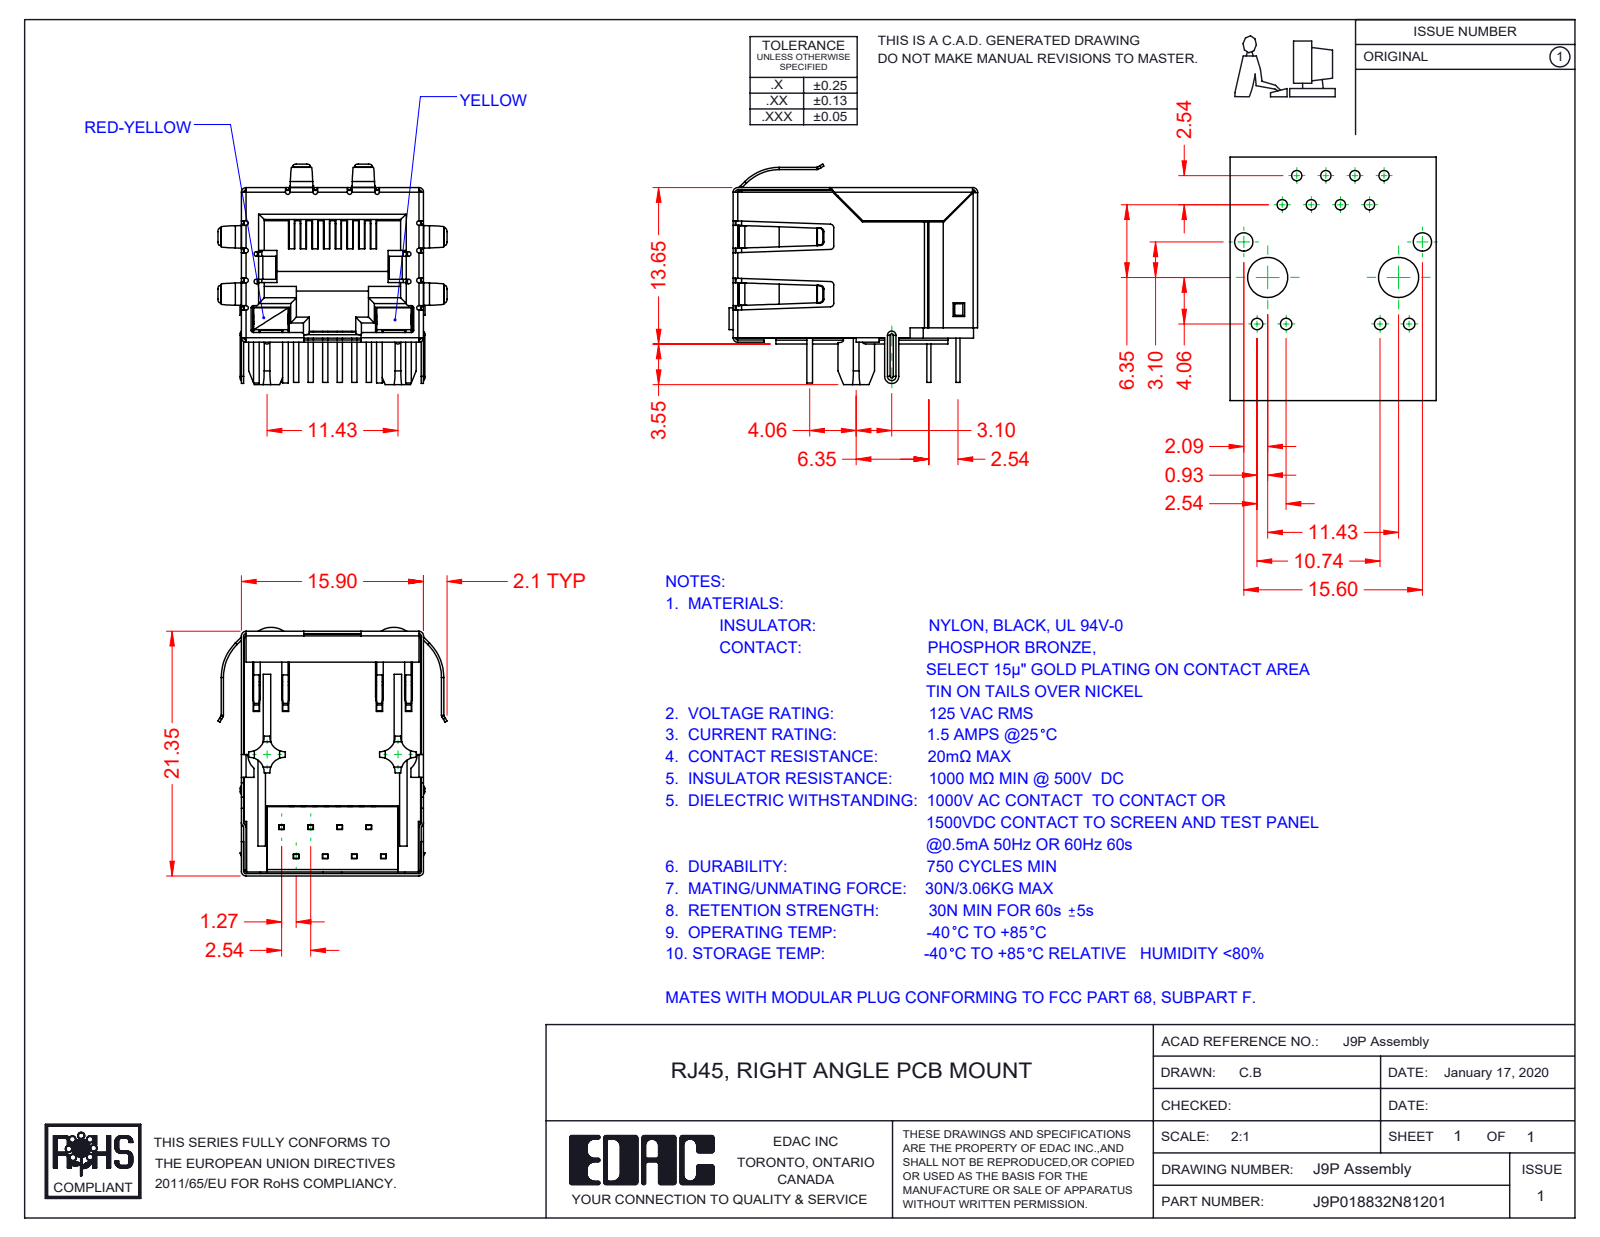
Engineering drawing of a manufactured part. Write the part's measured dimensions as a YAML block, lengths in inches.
part_name: "9P-LED Assembly; 9P-LED Contacts; 9P-LED LED LH_8-Red-Yellow; 9P-LED Shield (+4 more)"
step_written_by: "SolidWorks 2016 (CONFIG_CONTROL_DESIGN)"
units: inches
bodies: {solids: 13, faces: 1474, planar: 1042, cylindrical: 338, other: 94}
overall_size: [0.854, 0.787, 0.758]
volume: 0.164
surface_area: 11.65
partial_cylinders:
  - {radius: 0.008, count: 39}
  - {radius: 0.02, count: 22}
  - {radius: 0.012, count: 20}
  - {radius: 0.016, count: 16}
  - {radius: 0.051, count: 8}
  - {radius: 0.009, count: 5}
  - {radius: 0.004, count: 4}
  - {radius: 0.012, count: 4}
face_to_face_distances: [0.608, 0.618, 0.616, 0.014, 0.021, 0.61, 0.487, 0.024, 0.055, 0.023]
